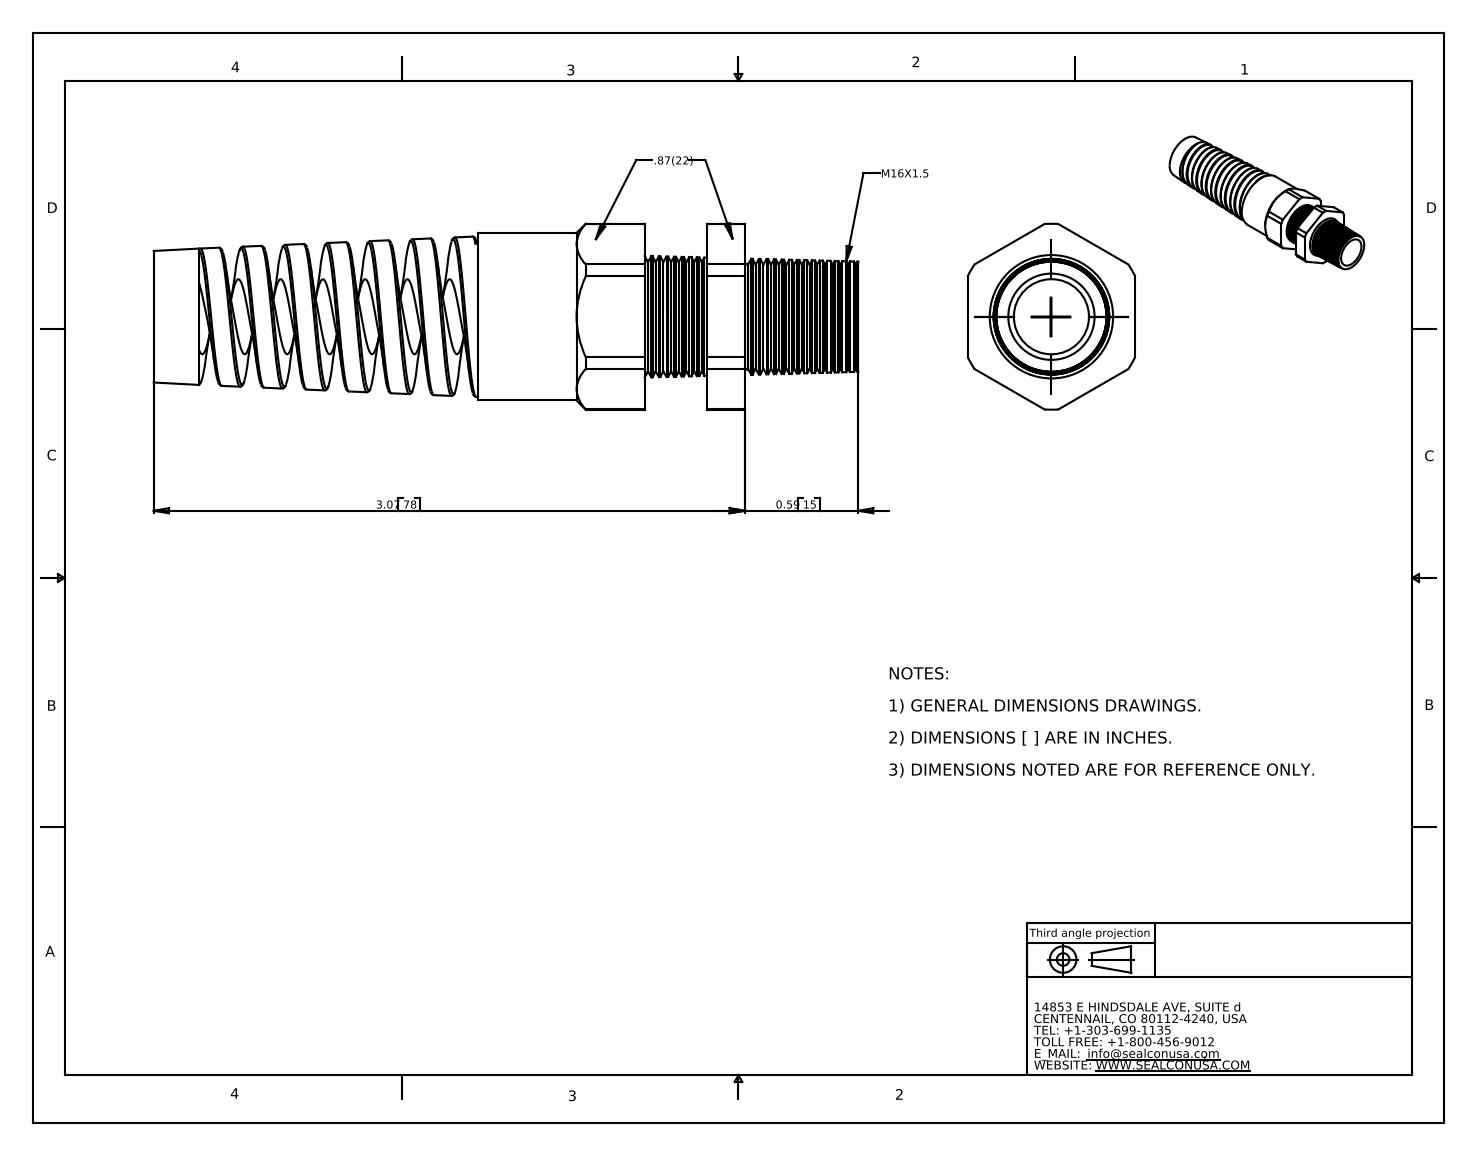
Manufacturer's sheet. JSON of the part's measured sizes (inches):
{"part_name": "CF17DA-GY", "step_written_by": "SolidWorks 2007 (CONFIG_CONTROL_DESIGN)", "units": "inches", "bodies": {"solids": 2, "faces": 239, "planar": 25, "cylindrical": 39, "other": 175}, "overall_size": [3.66, 0.966, 0.87], "volume_in3": 1.011, "surface_area_in2": 19.2, "round_holes": [[0.39, 1], [0.415, 1]], "round_bosses_or_shafts": [[0.87, 1], [0.635, 1]], "partial_cylinders_radius": [[0.483, 1]], "face_to_face_distances": [0.87, 0.323, 0.52, 0.197, 2.55, 2.873, 3.07, 1.682, 0.869, 1.191]}
